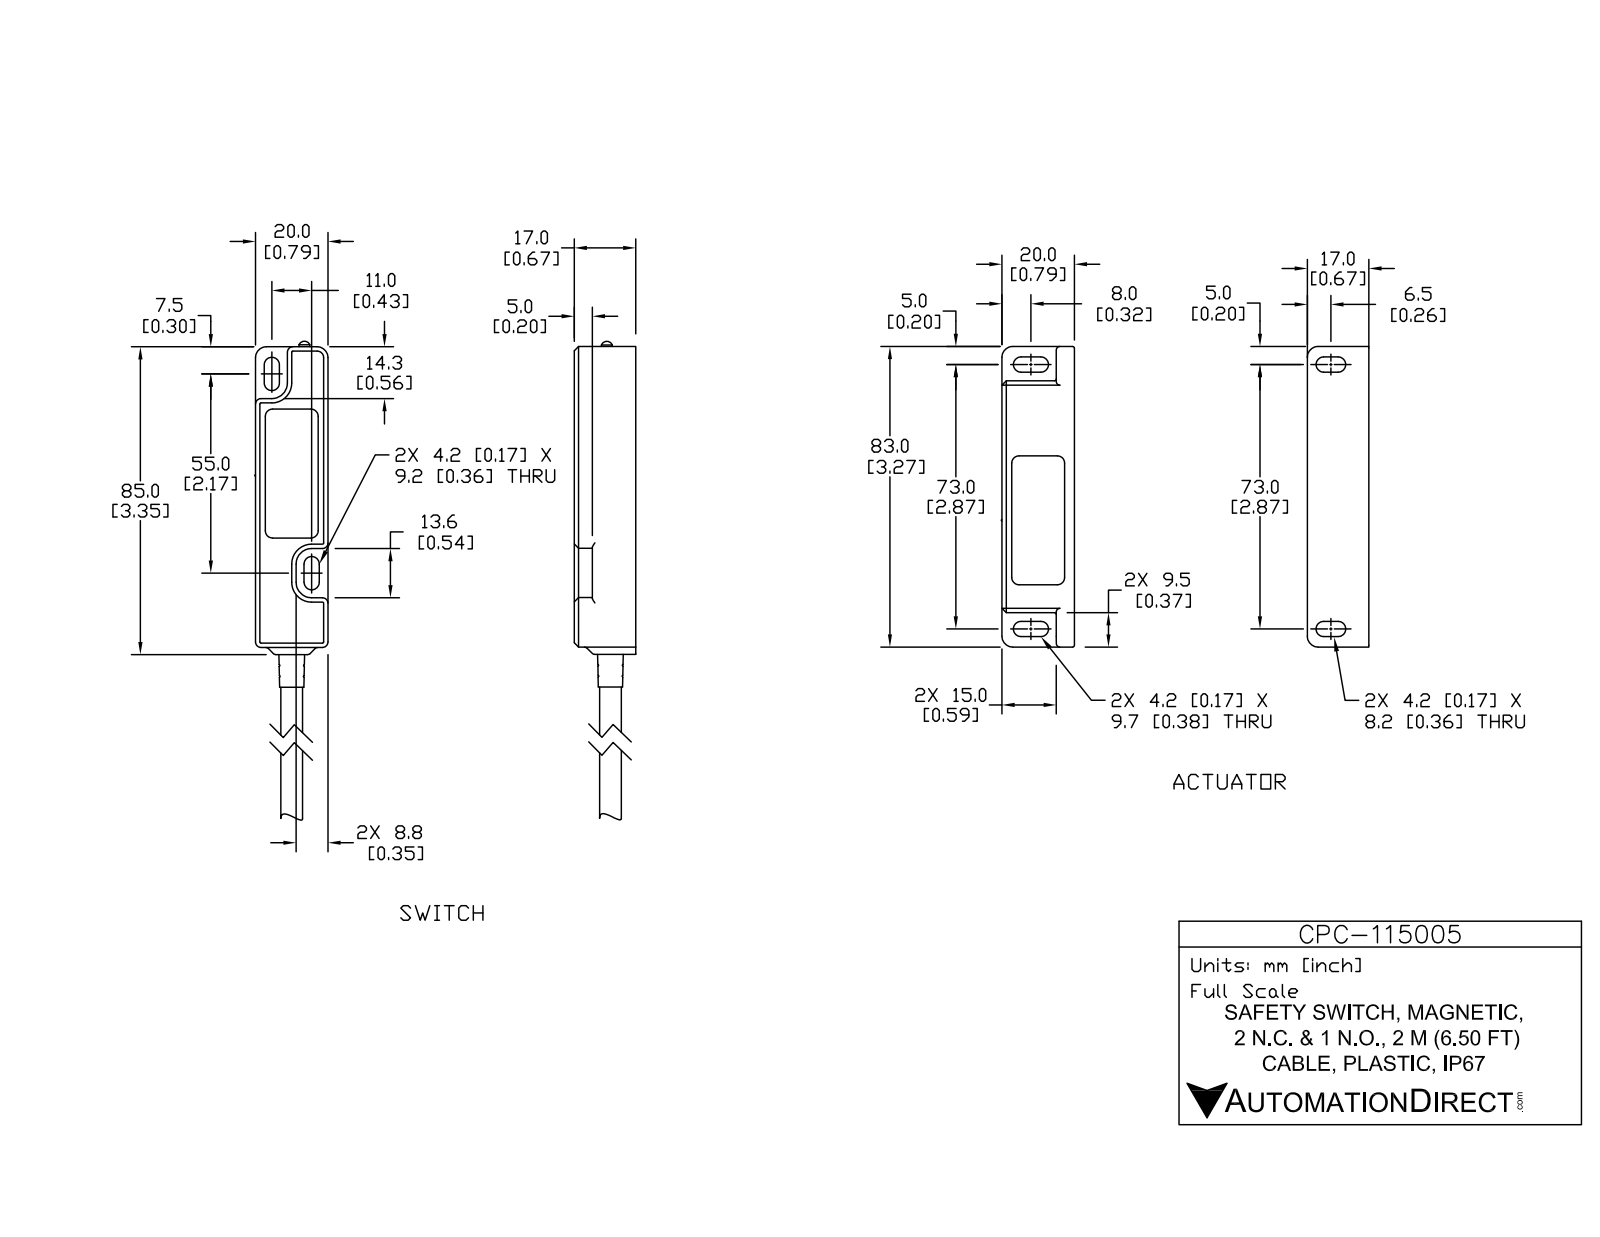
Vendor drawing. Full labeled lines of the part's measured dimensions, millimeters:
Part name (STEP PRODUCT): CPC-115005; CPC-115005_1; CPC-115005_2
STEP written by: SolidWorks 2017 (AUTOMOTIVE_DESIGN)
Units: millimetres
Bodies: 5 solids, 199 faces (78 planar, 71 cylindrical, 50 other)
Overall size (bounding box): 184.6 × 41 × 17
Volume: 53 130 mm³ · Surface area: 16 220 mm²
Round bosses / shafts (diameter × count): ⌀6 ×1, ⌀3 ×1
Partial cylindrical surfaces — rounded edges, fillets, slot ends (radius × count): R2.1 ×12, R1 ×10, R0.5 ×8, R2 ×8, R1.5 ×6, R3 ×6, R0.7 ×3, R4.3 ×3
Main face-to-face distances: 21, 20, 17, 41, 16.7, 1, 5, 12, 9.5, 73.5
